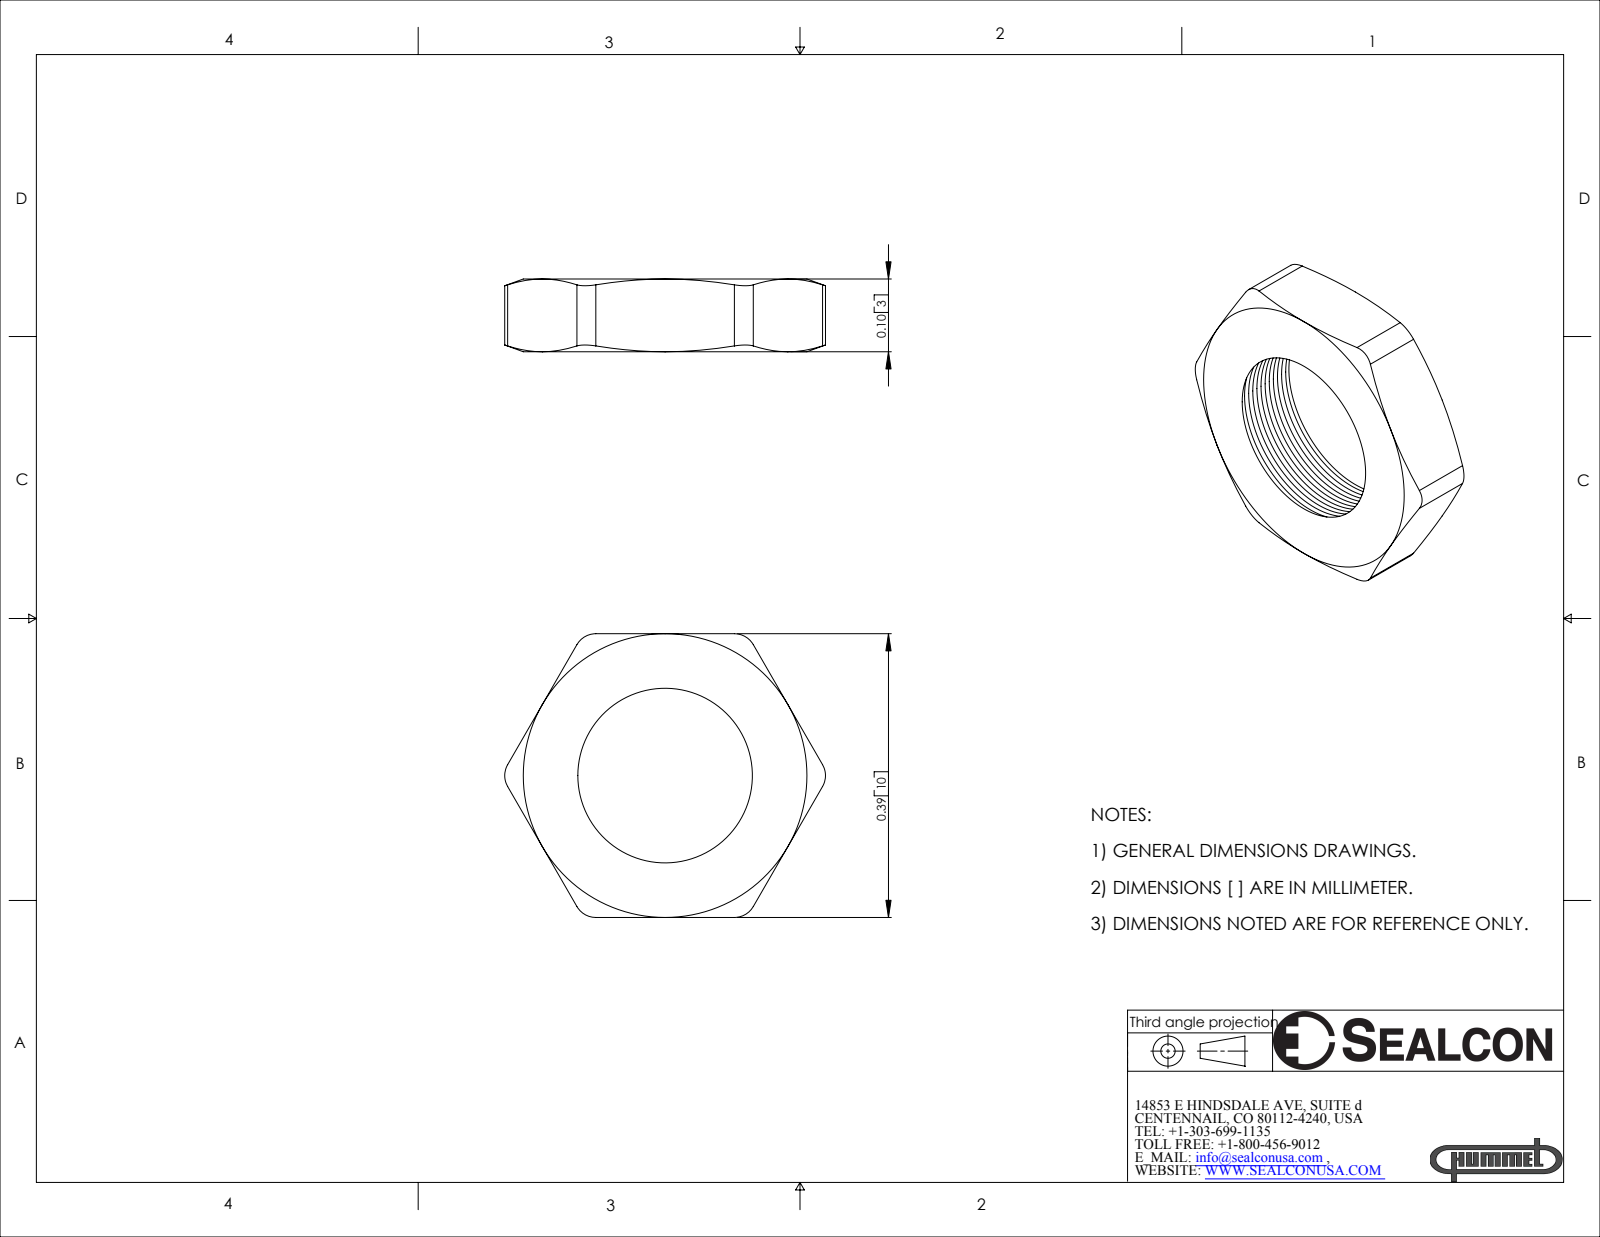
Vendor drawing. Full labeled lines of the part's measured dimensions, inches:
Part name (STEP PRODUCT): NM-06-BR
STEP written by: SolidWorks 2007 (CONFIG_CONTROL_DESIGN)
Units: inches
Bodies: 1 solid, 77 faces (8 planar, 7 cylindrical, 62 other)
Overall size (bounding box): 0.441 × 0.39 × 0.1
Volume: 0.008 in³ · Surface area: 0.455 in²
Partial cylindrical surfaces — rounded edges, fillets, slot ends (radius × count): R0.03 ×6
Main face-to-face distances: 0.1, 0.39
